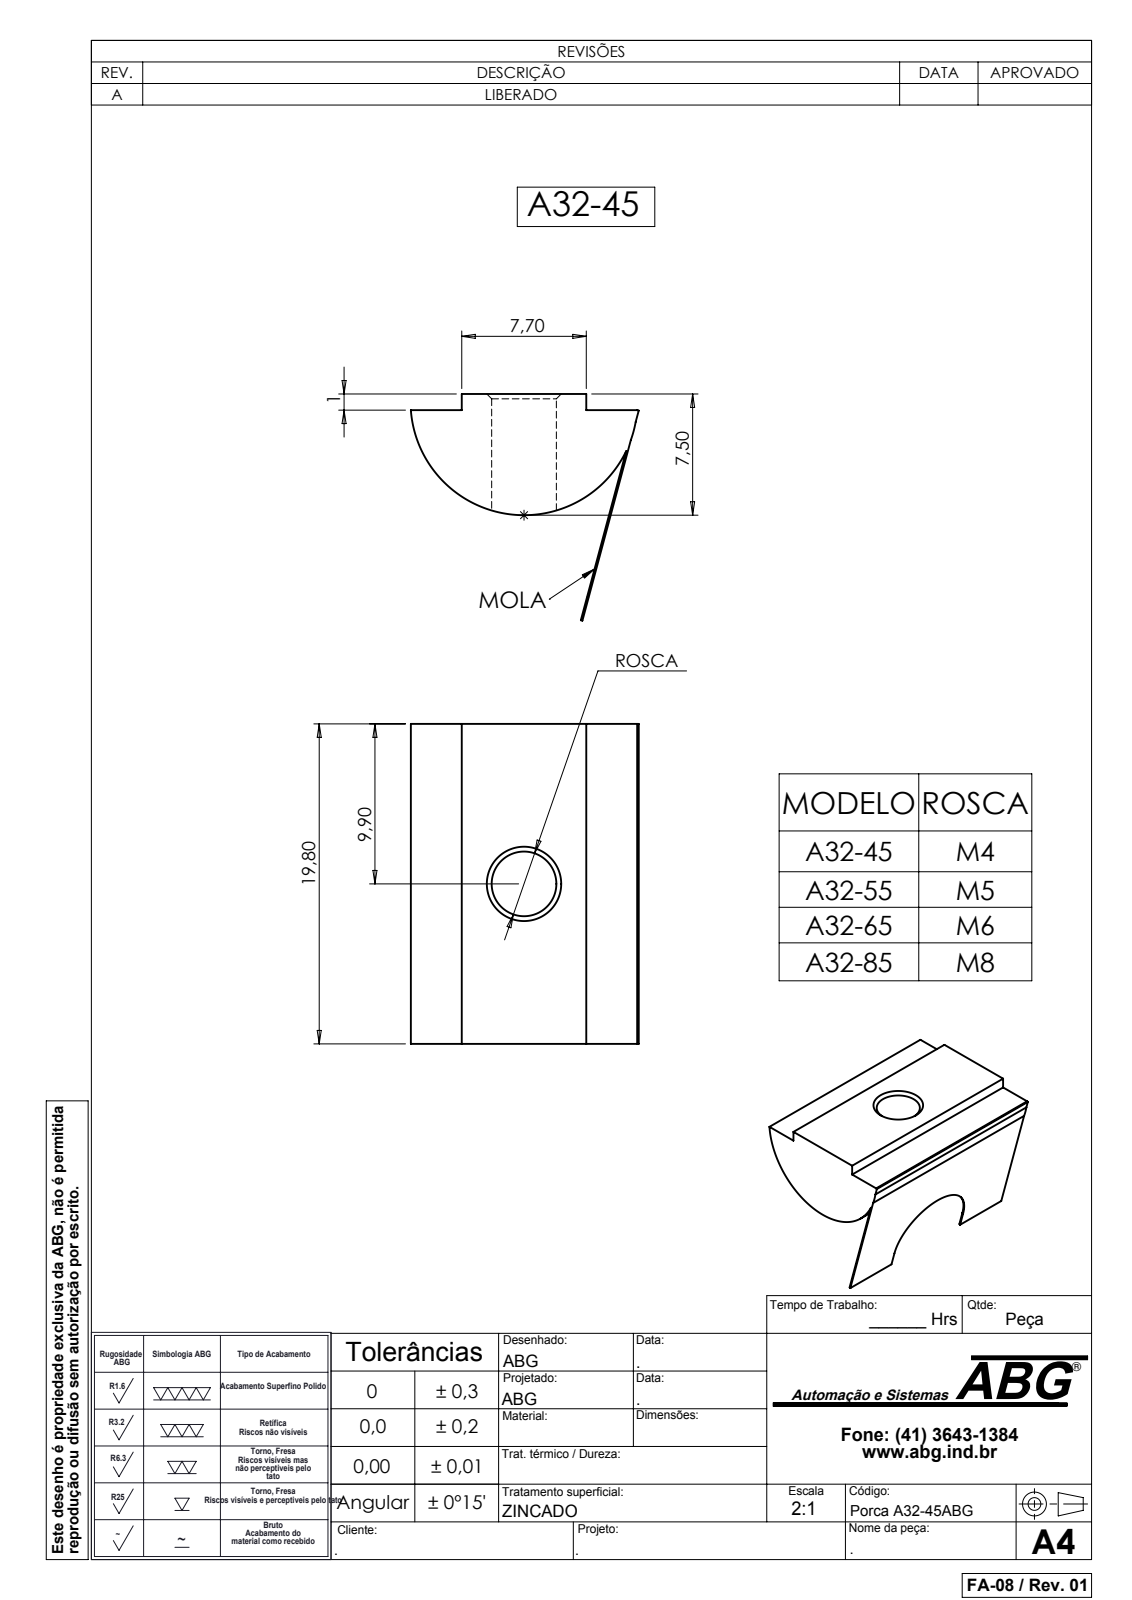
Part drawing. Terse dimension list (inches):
name: A32-45
written by: SolidWorks 2007 (CONFIG_CONTROL_DESIGN)
unit: in
bodies: 1 solid, 22 faces (15 planar, 5 cylindrical, 2 other)
size: 0.78 × 0.555 × 0.552
volume: 0.089 in³; area: 2.013 in²
holes: 1× ⌀0.157
rounds: 1× R0.177, 1× R0.276
face distances: 0.039, 0.78, 0.303, 0.53, 0.213, 0.567, 0.354
